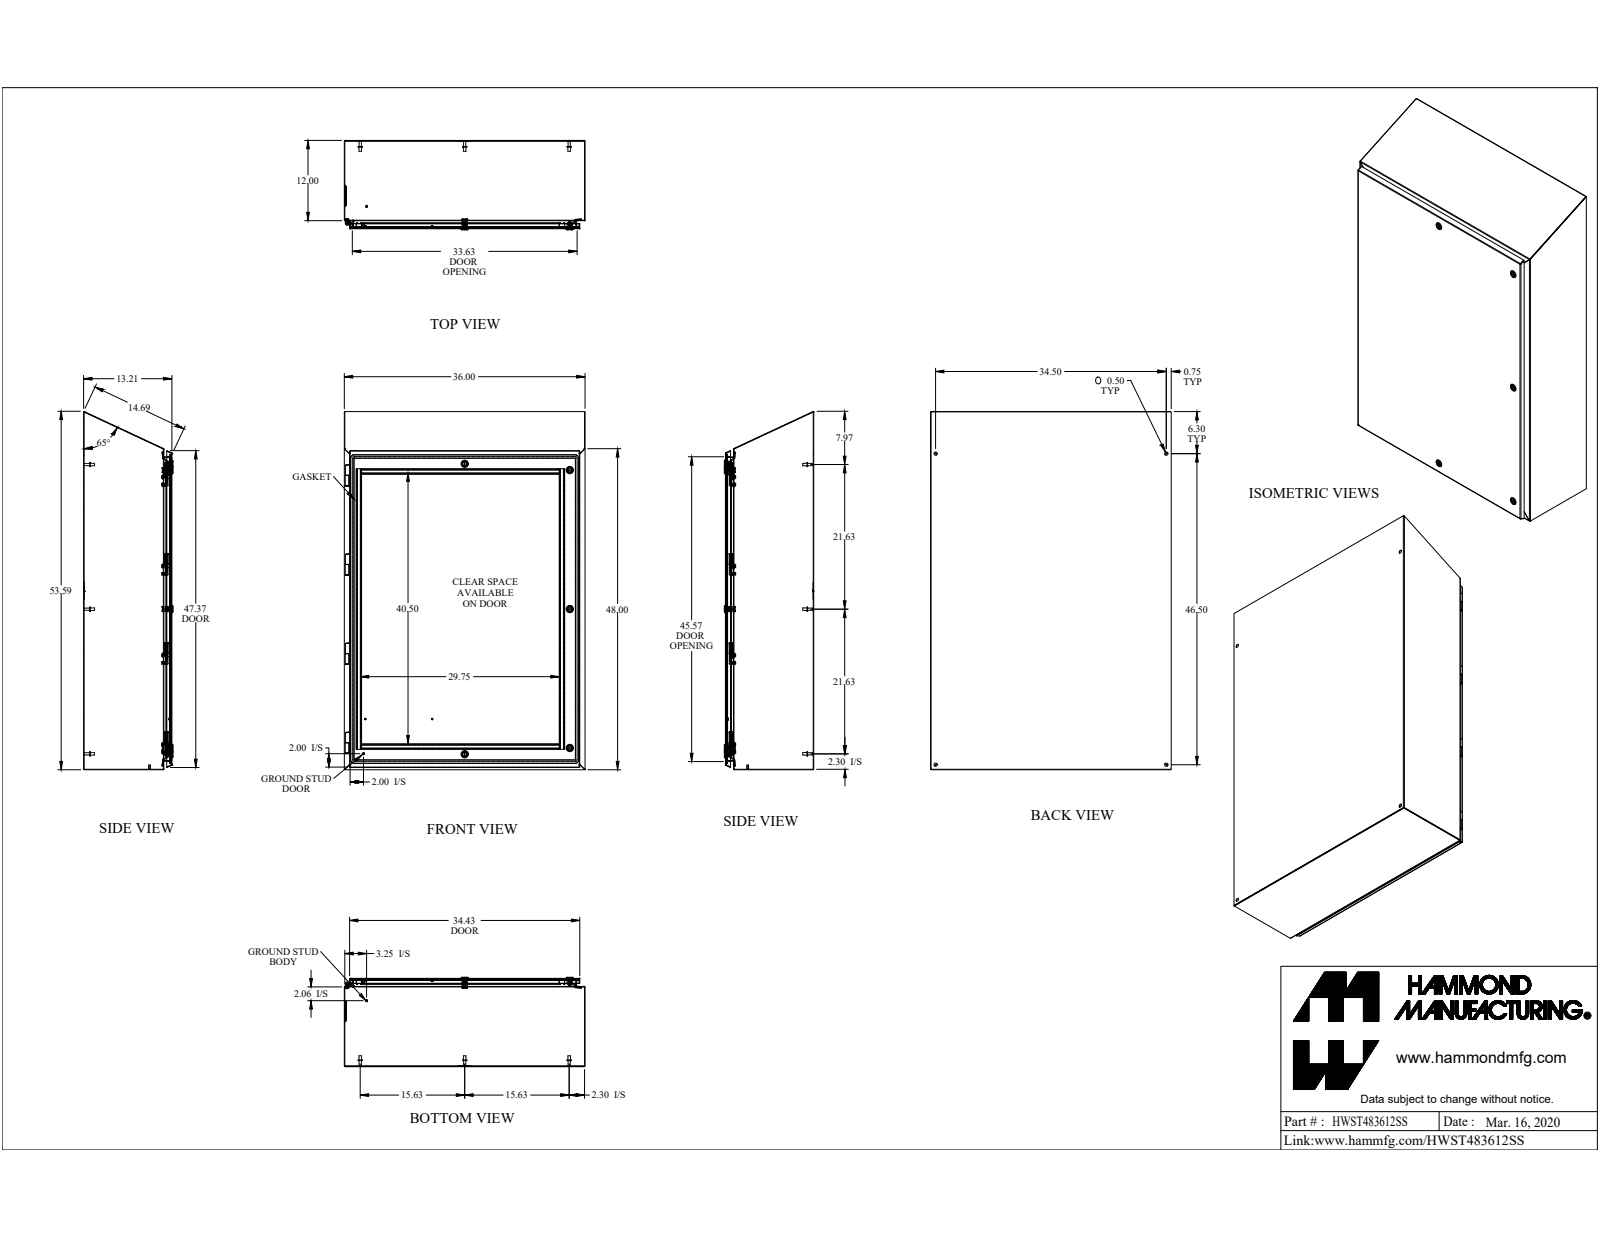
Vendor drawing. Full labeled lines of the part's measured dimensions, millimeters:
Part name (STEP PRODUCT): HWST483612SS
STEP written by: SolidWorks 2019 (AUTOMOTIVE_DESIGN)
Units: millimetres
Bodies: 86 solids, 2051 faces (1256 planar, 559 cylindrical, 236 other)
Overall size (bounding box): 1360 × 914.4 × 339.6
Volume: 8 020 000 mm³ · Surface area: 8 883 000 mm²
Round holes (diameter × count): ⌀4.9 ×16, ⌀6.1 ×16, ⌀12.7 ×9, ⌀7 ×8, ⌀5 ×5, ⌀9.8 ×5, ⌀16 ×5, ⌀19.5 ×5, ⌀3.3 ×2, ⌀6.1 ×1, ⌀88.9 ×1
Round bosses / shafts (diameter × count): ⌀5.7 ×16, ⌀15.9 ×12, ⌀16.5 ×8, ⌀9.5 ×8, ⌀8.4 ×8, ⌀6 ×6, ⌀27.9 ×5, ⌀19.9 ×4
Partial cylindrical surfaces — rounded edges, fillets, slot ends (radius × count): R1 ×32, R3.2 ×26, R1.1 ×24, R6.4 ×24, R0.3 ×20, R0.9 ×17, R2.7 ×17, R0.8 ×16
Main face-to-face distances: 1.8, 1.8, 333.7, 331.9, 333.7, 335.5, 910.7, 912.6, 912.6, 914.4
Hole centre spacings: 29, 338.5, 338.4, 338.5, 338.4, 367.5, 676.9, 676.9
